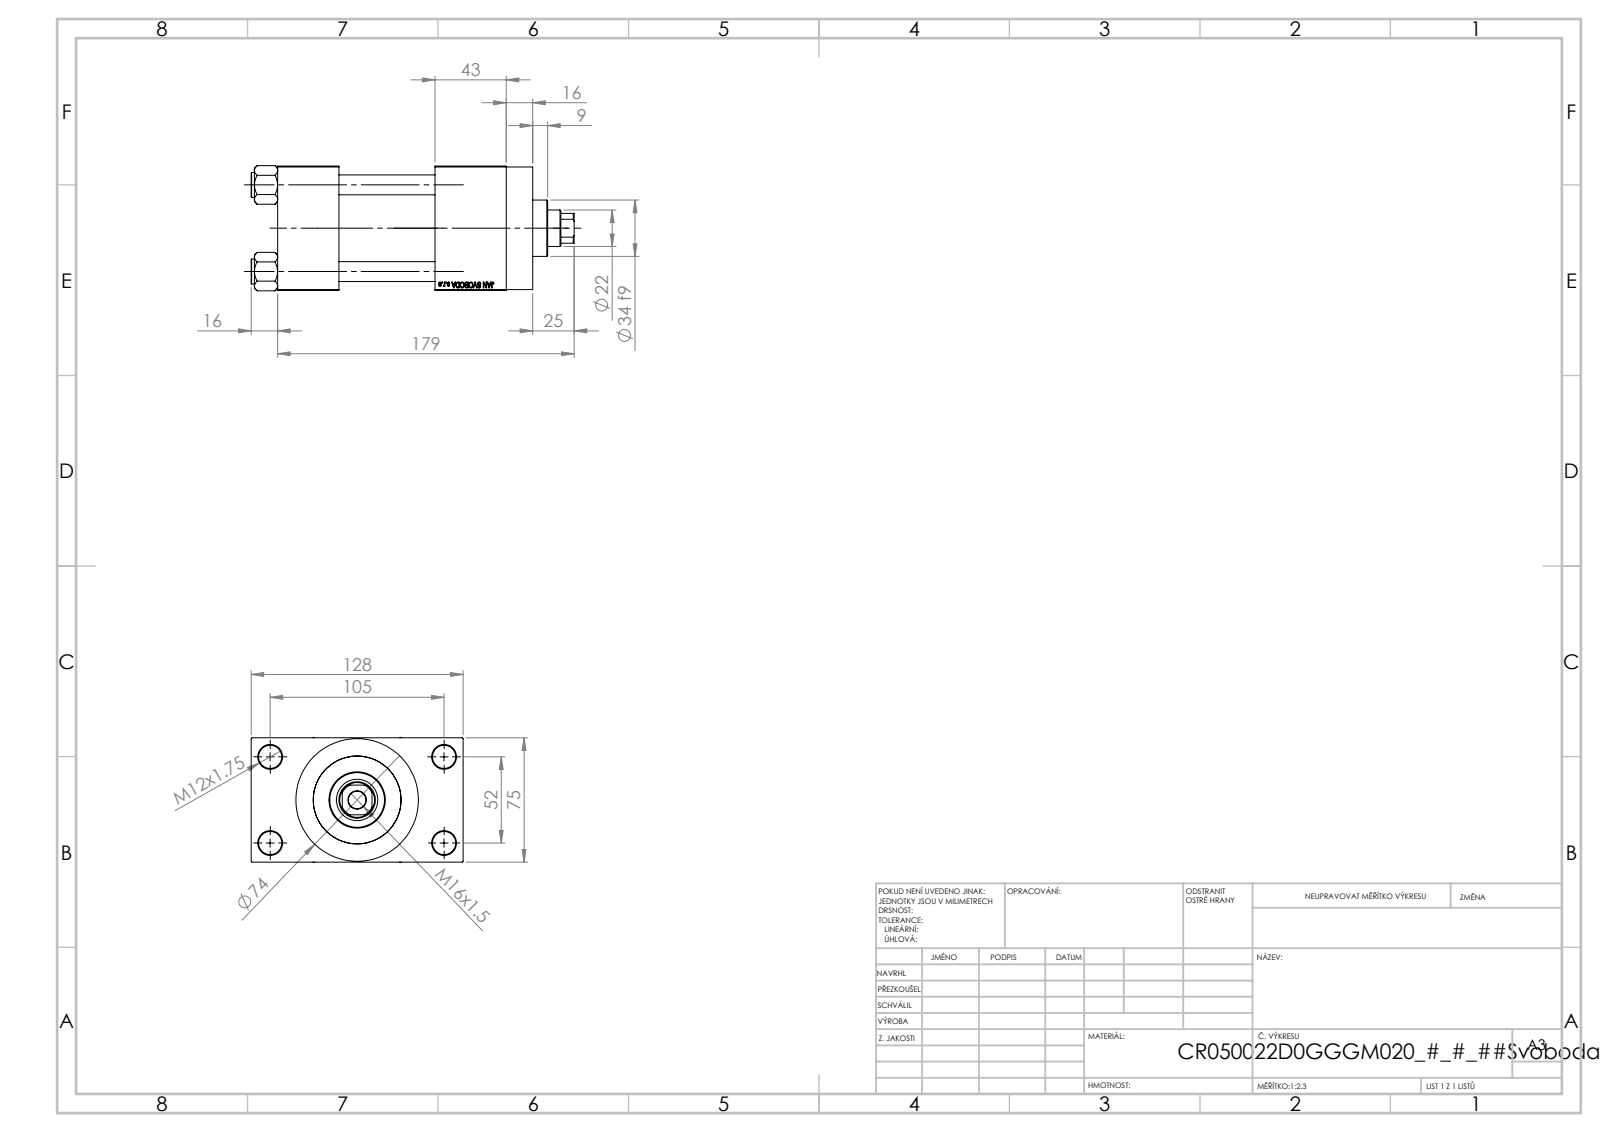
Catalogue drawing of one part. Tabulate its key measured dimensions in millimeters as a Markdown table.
| quantity | value |
| --- | --- |
| part name | V215_VC_A; V215CR_VCP_D; V215CR_D_Body; V215CR_D_TYCINKA (+1 more) |
| STEP written by | SolidWorks 2019 (CONFIG_CONTROL_DESIGN) |
| units | millimeters |
| bodies | 11 solids, 1104 faces (497 planar, 89 cylindrical, 518 other) |
| overall size | 195 × 128 × 75.54 |
| volume | 806 540 mm³ |
| surface area | 164 947 mm² |
| round holes (diameter × count) | 12 × 4, 14 × 4, 7 × 2, 20.96 × 2, 30 × 2, 10.5 × 1, 22 × 1, 25 × 1, 41 × 1, 50 × 1, 53 × 1 |
| round bosses / shafts (diameter × count) | 15 × 4, 74 × 1, 56 × 1, 34 × 1 |
| partial cylindrical surfaces (radius × count) | 10.5 × 1 |
| main face-to-face distances | 75, 58, 37, 95, 26.5, 101.5, 138, 101, 43, 16 |
| hole center spacings | 26.35, 36.98, 52.3, 58.43, 58.59, 78.65, 94.37, 52 |
